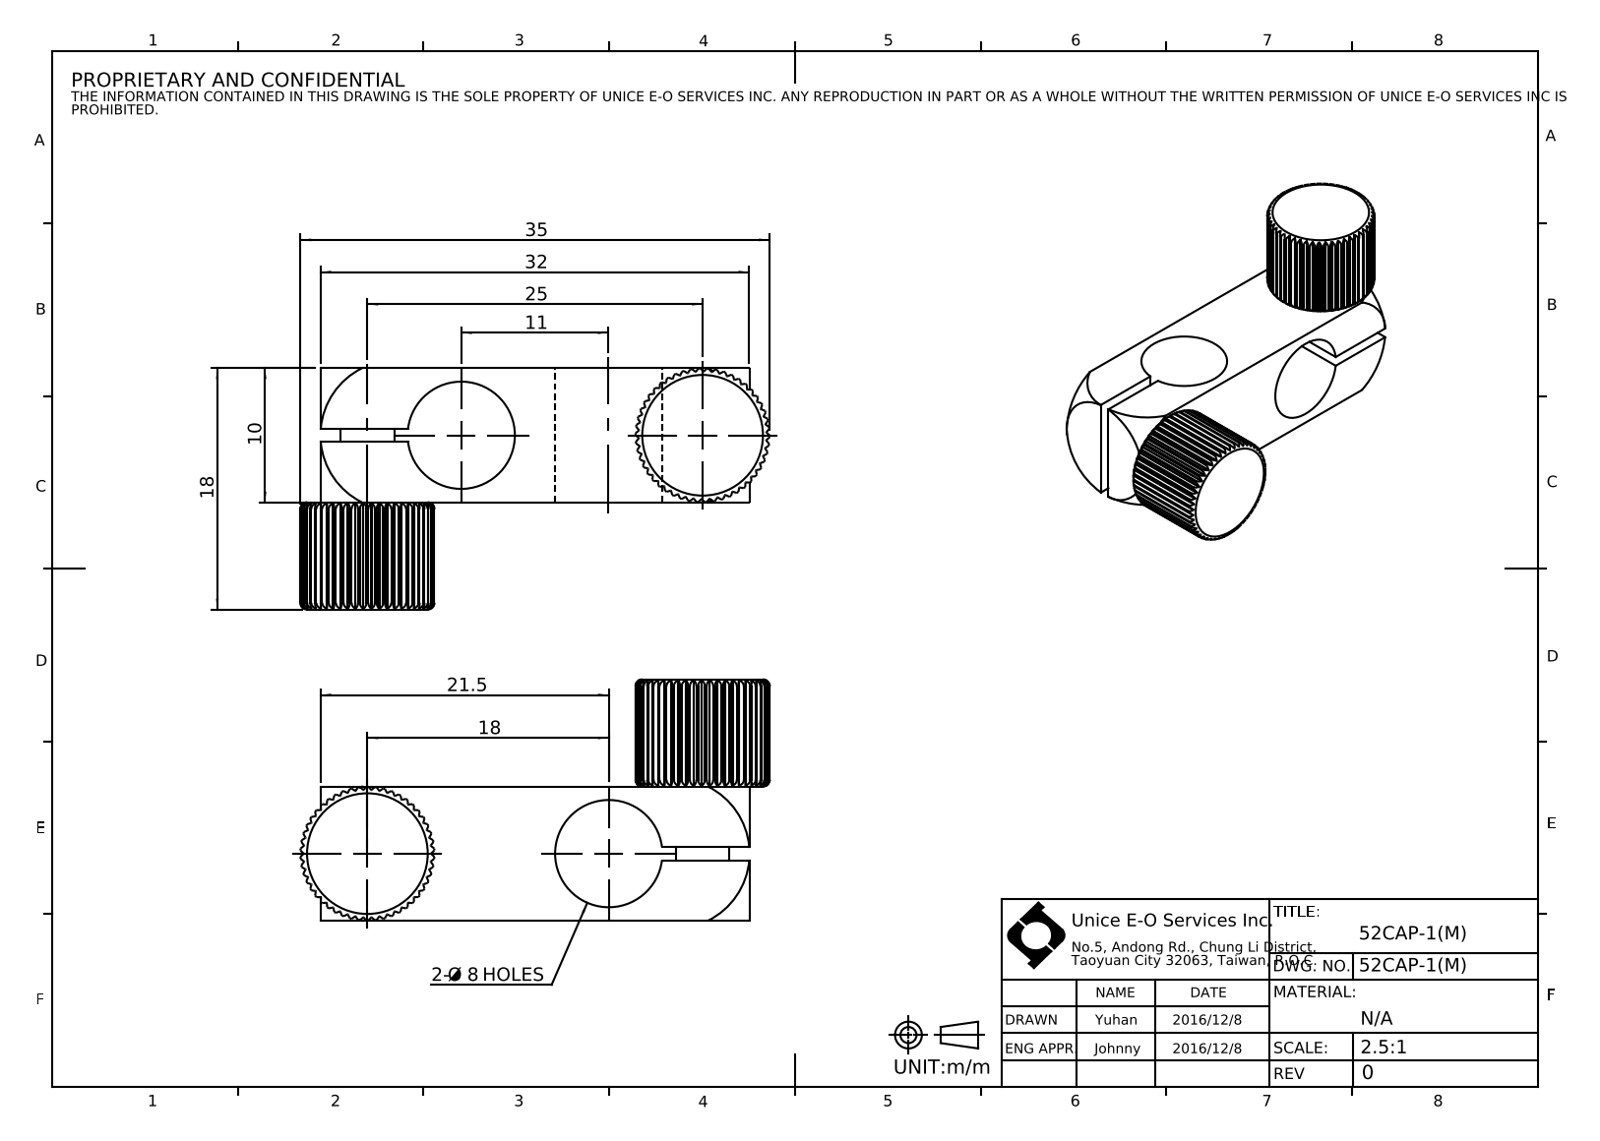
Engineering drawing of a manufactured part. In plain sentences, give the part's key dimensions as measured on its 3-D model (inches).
The part is named "52CAP-1(M)". Its 3-D file was written by "SolidWorks 2016 (CONFIG_CONTROL_DESIGN)". It is 3 solids with 480 faces: 218 planar, 242 cylindrical and 20 other. Overall it measures 1.378 by 0.709 by 0.709 inches. Its volume is 0.199 cubic inches and its surface area 5.005 square inches. Round holes: 2 of diameter 0.13, 2 of diameter 0.177, 2 of diameter 0.315. Round bosses or shafts: 2 of diameter 0.157. Partial cylindrical surfaces (rounded edges, fillets, slot ends): 2 of radius 0.197. The main face-to-face distances are 0.394, 0.217, 0.177, 0.265, 0.709, 0.315, 0.531, 0.492, 0.039, 0.264. The hole center spacings are 0.709.
